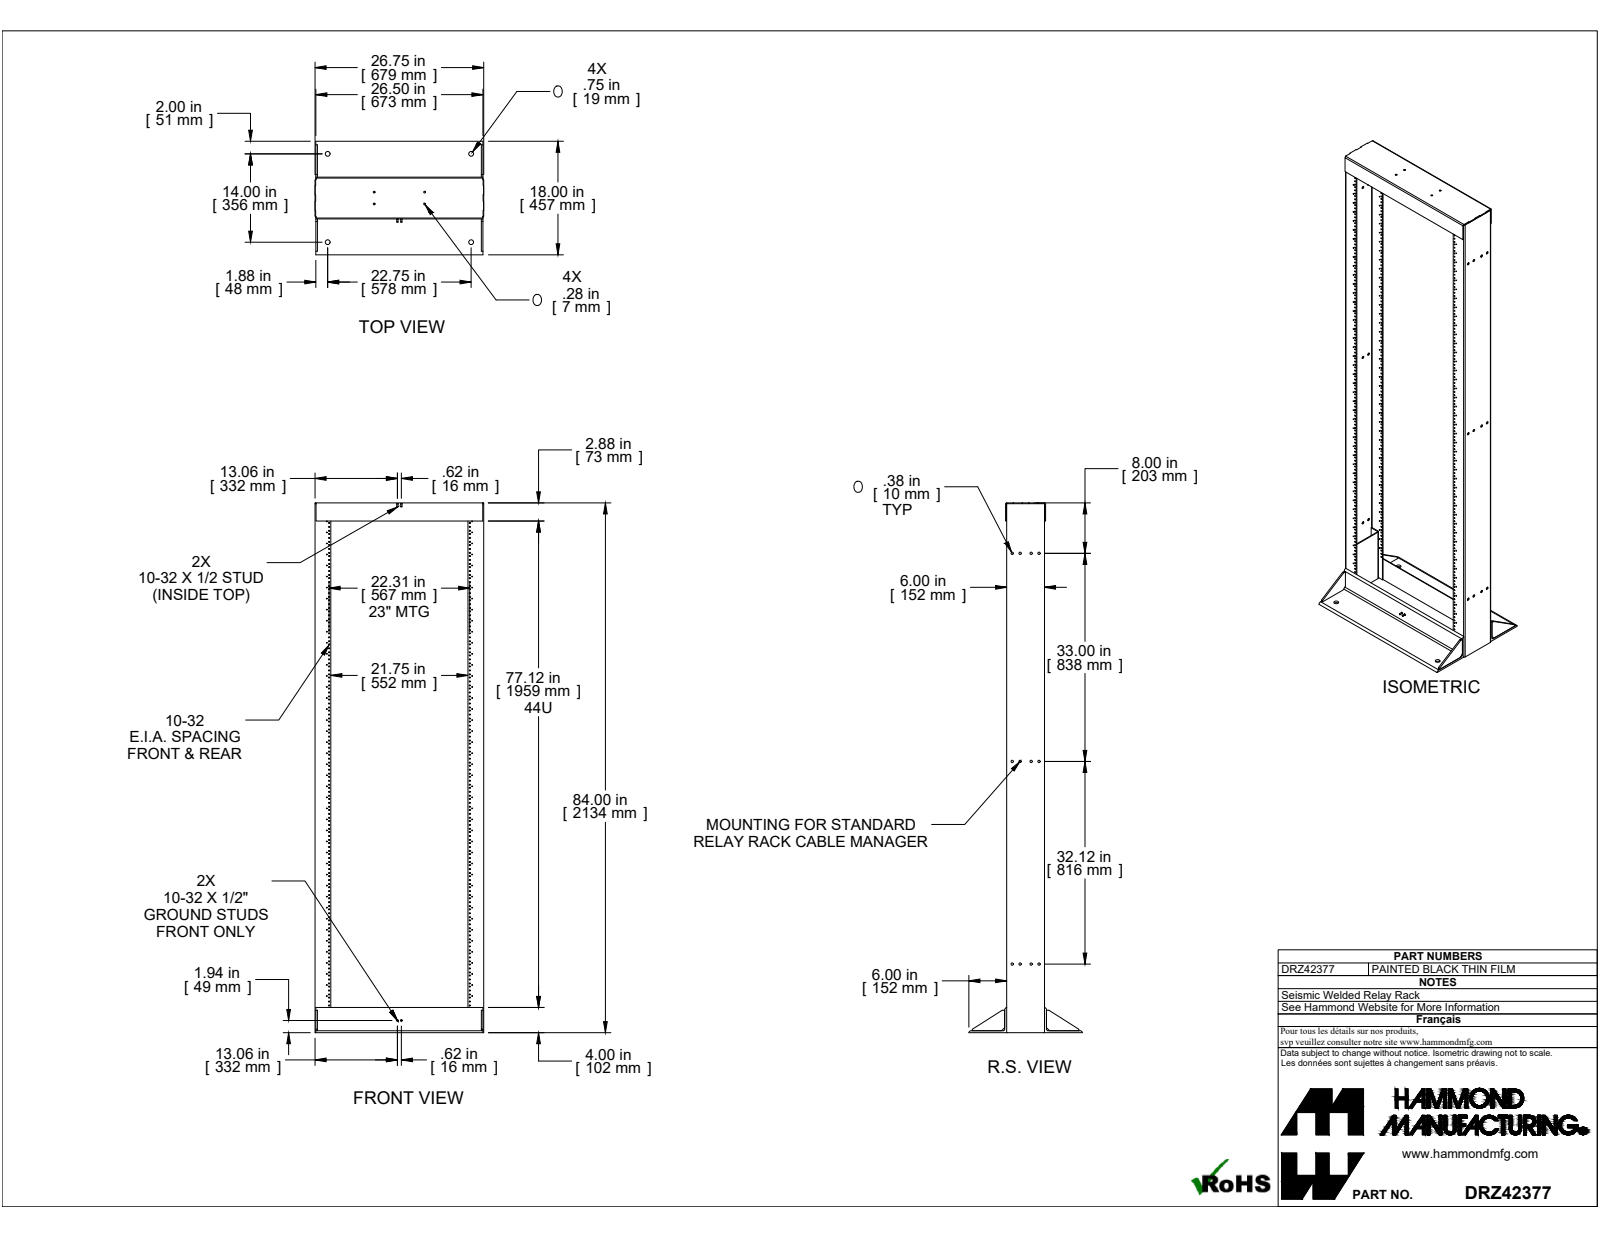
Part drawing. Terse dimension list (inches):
name: DRZ42377
written by: SolidWorks 2019 (CONFIG_CONTROL_DESIGN)
unit: in
bodies: 15 solids, 936 faces (138 planar, 794 cylindrical, 4 other)
size: 84 × 26.75 × 18
volume: 446.2 in³; area: 5 725 in²
holes: 274× ⌀0.177, 45× ⌀0.125, 45× ⌀0.125, 16× ⌀0.375, 4× ⌀0.281, 4× ⌀0.75
bosses: 4× ⌀0.25, 4× ⌀0.188
rounds: 4× R0.048, 4× R0.1, 4× R0.173, 4× R0.225, 2× R0.06, 2× R0.185, 2× R0.25, 2× R0.386
face distances: 0.125, 0.125, 26.5, 6, 26.625, 26.625, 26.75, 5.875, 5.875, 5.75
hole spacings: 1.75, 3.5, 1.25, 3, 5.25, 7, 8.75, 10.5
